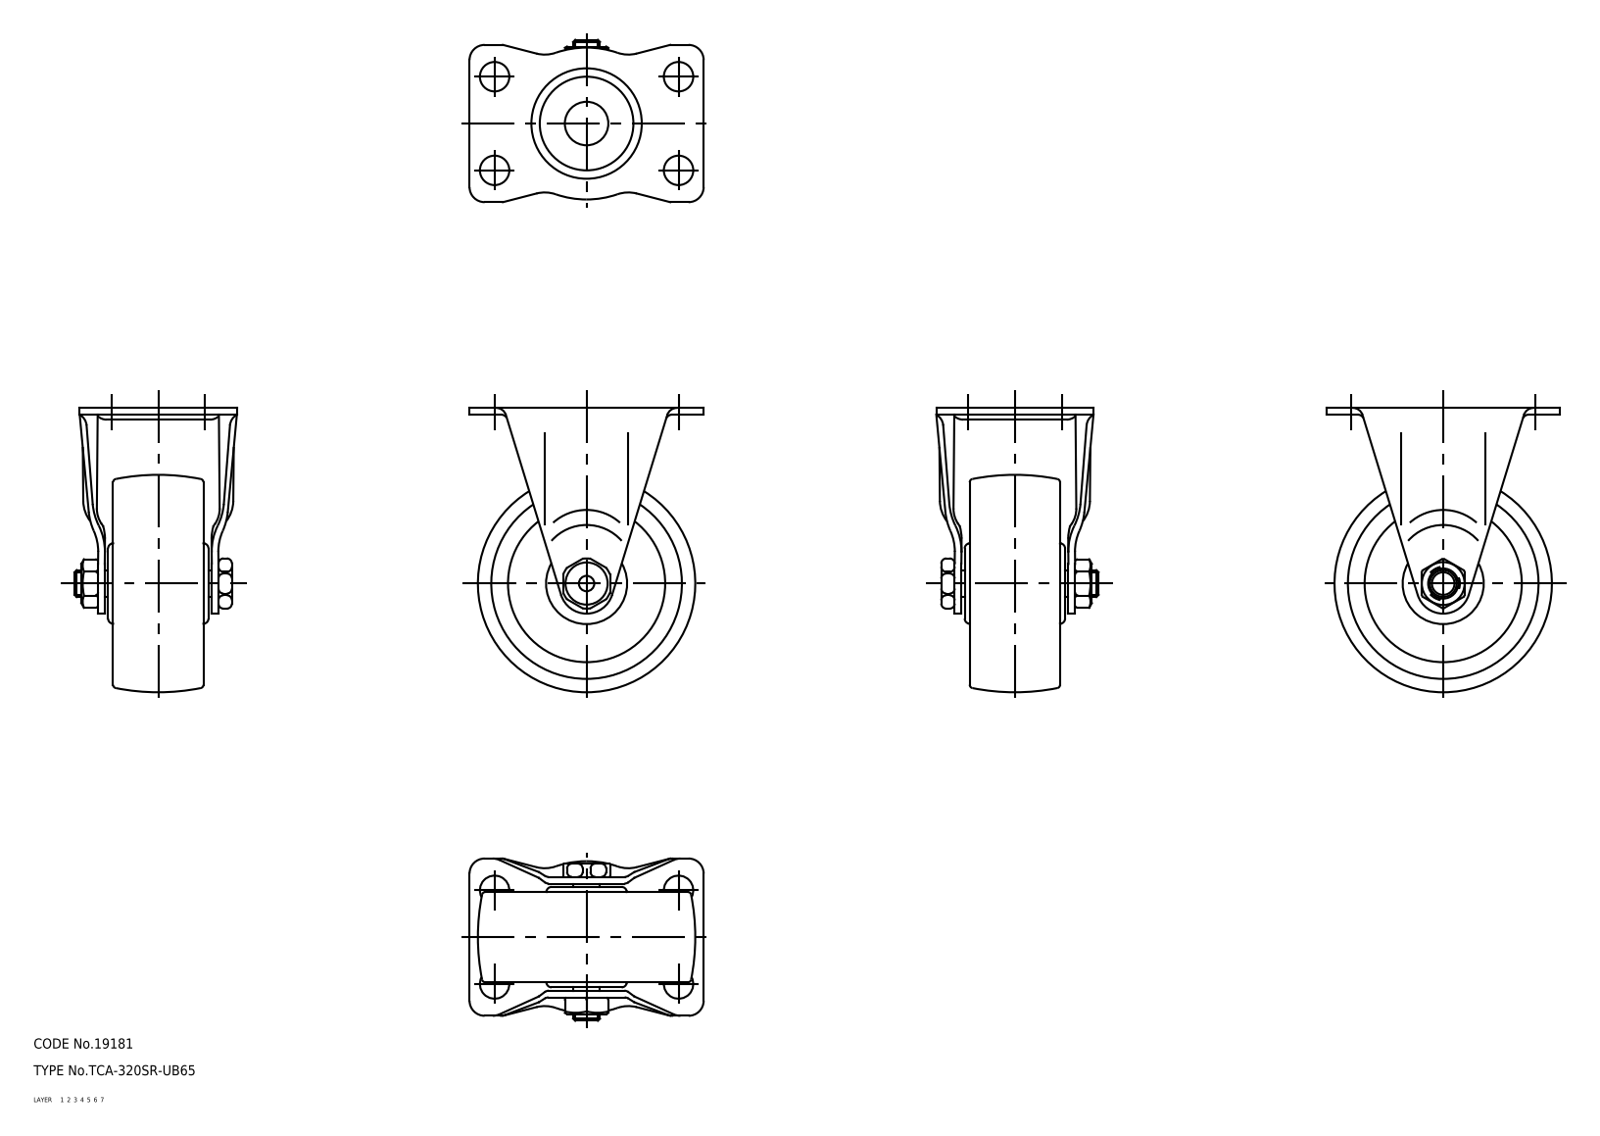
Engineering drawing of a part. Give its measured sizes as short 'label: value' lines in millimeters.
name: wheel; axle; 320SR_UB65_9500_36
written by: CADfix (AUTOMOTIVE_DESIGN)
unit: mm
bodies: 3 solids, 250 faces (0 planar, 0 cylindrical, 250 other)
size: 85 × 70 × 48.49
volume: 90 268 mm³; area: 30 024 mm²
